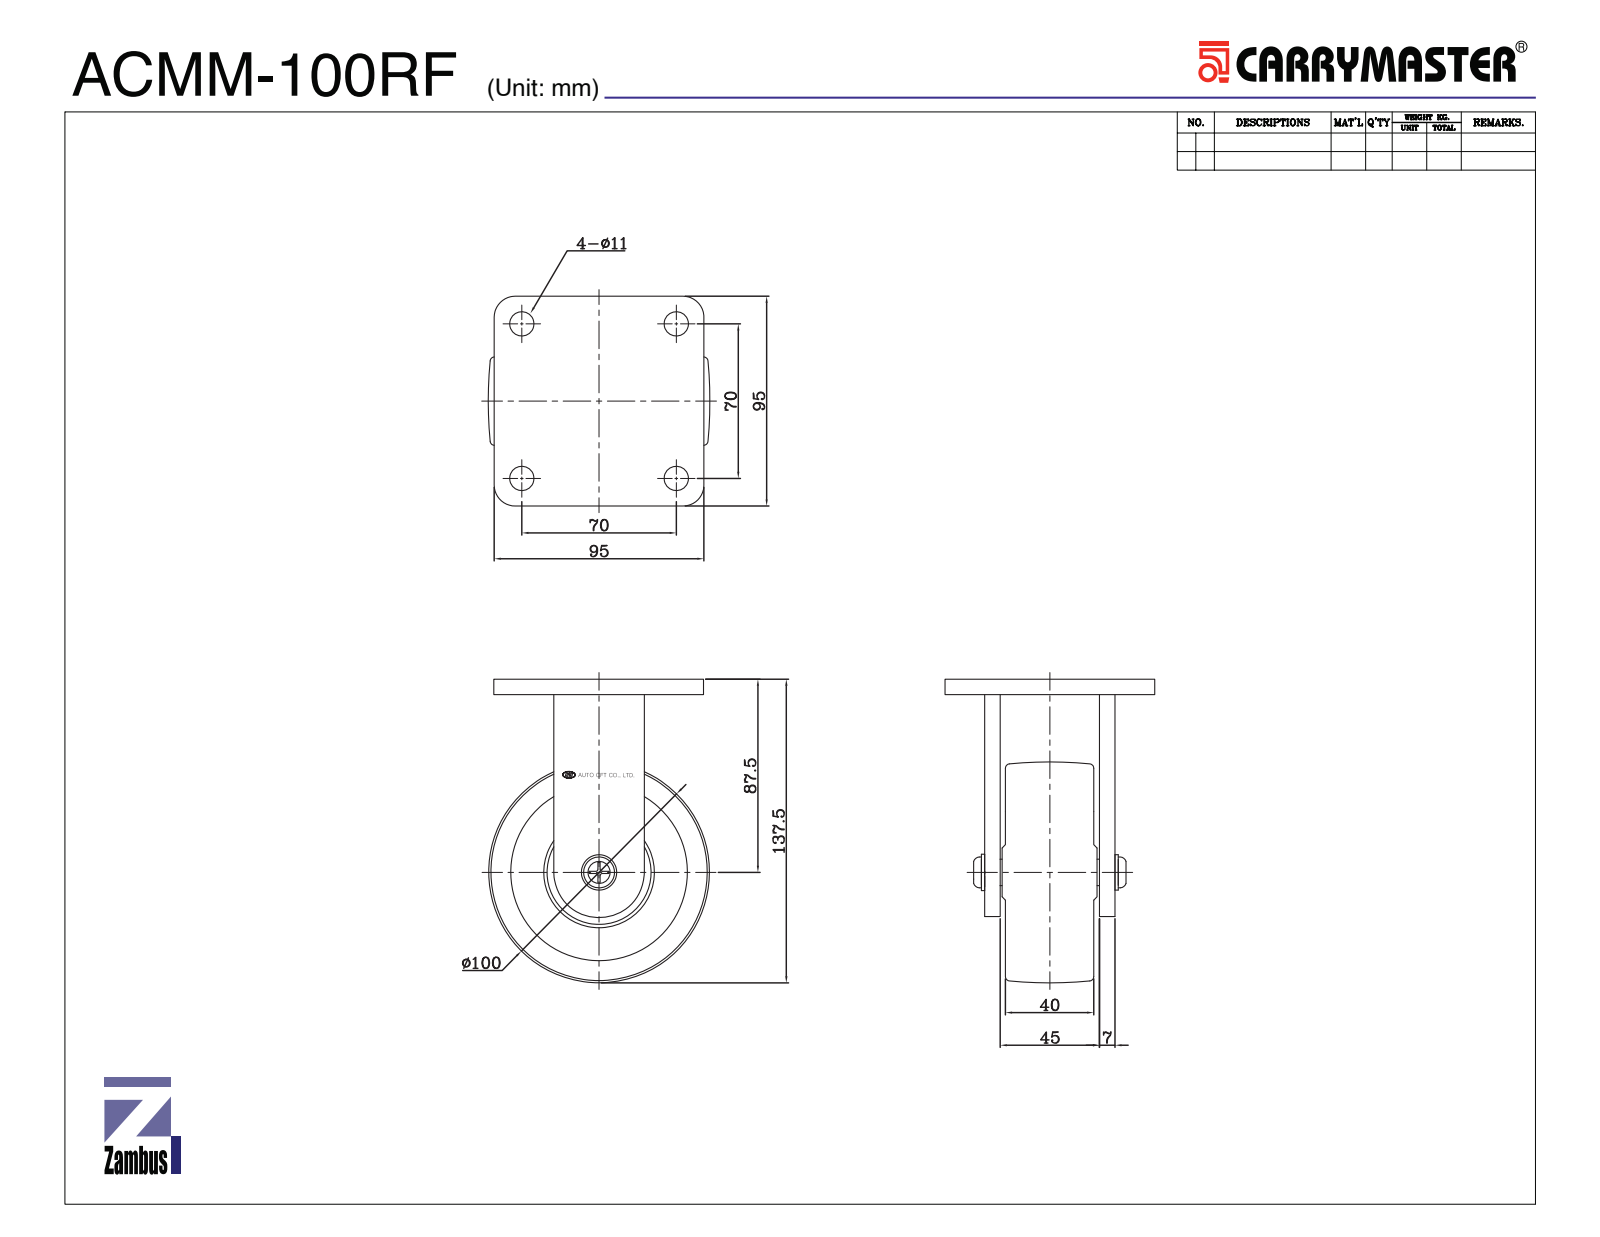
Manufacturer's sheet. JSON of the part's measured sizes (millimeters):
{"part_name": "ACMM-100RF", "step_written_by": "SolidWorks 2015 (CONFIG_CONTROL_DESIGN)", "units": "millimeters", "bodies": {"solids": 6, "faces": 721, "planar": 202, "cylindrical": 57, "other": 462}, "overall_size": [137.5, 100, 95], "volume_mm3": 396171, "surface_area_mm2": 75250, "round_holes": [[11, 4], [6.8, 1], [12.3, 1], [31.1, 1], [37, 1]], "round_bosses_or_shafts": [[16, 1], [14, 1], [12, 1], [8, 1]], "partial_cylinders_radius": [[9.5, 4], [0.52, 2], [20.5, 1]], "face_to_face_distances": [7, 9.5, 49.5, 2.5, 52, 42.5, 40, 59, 45, 51], "hole_center_spacings": [70, 98.99]}
